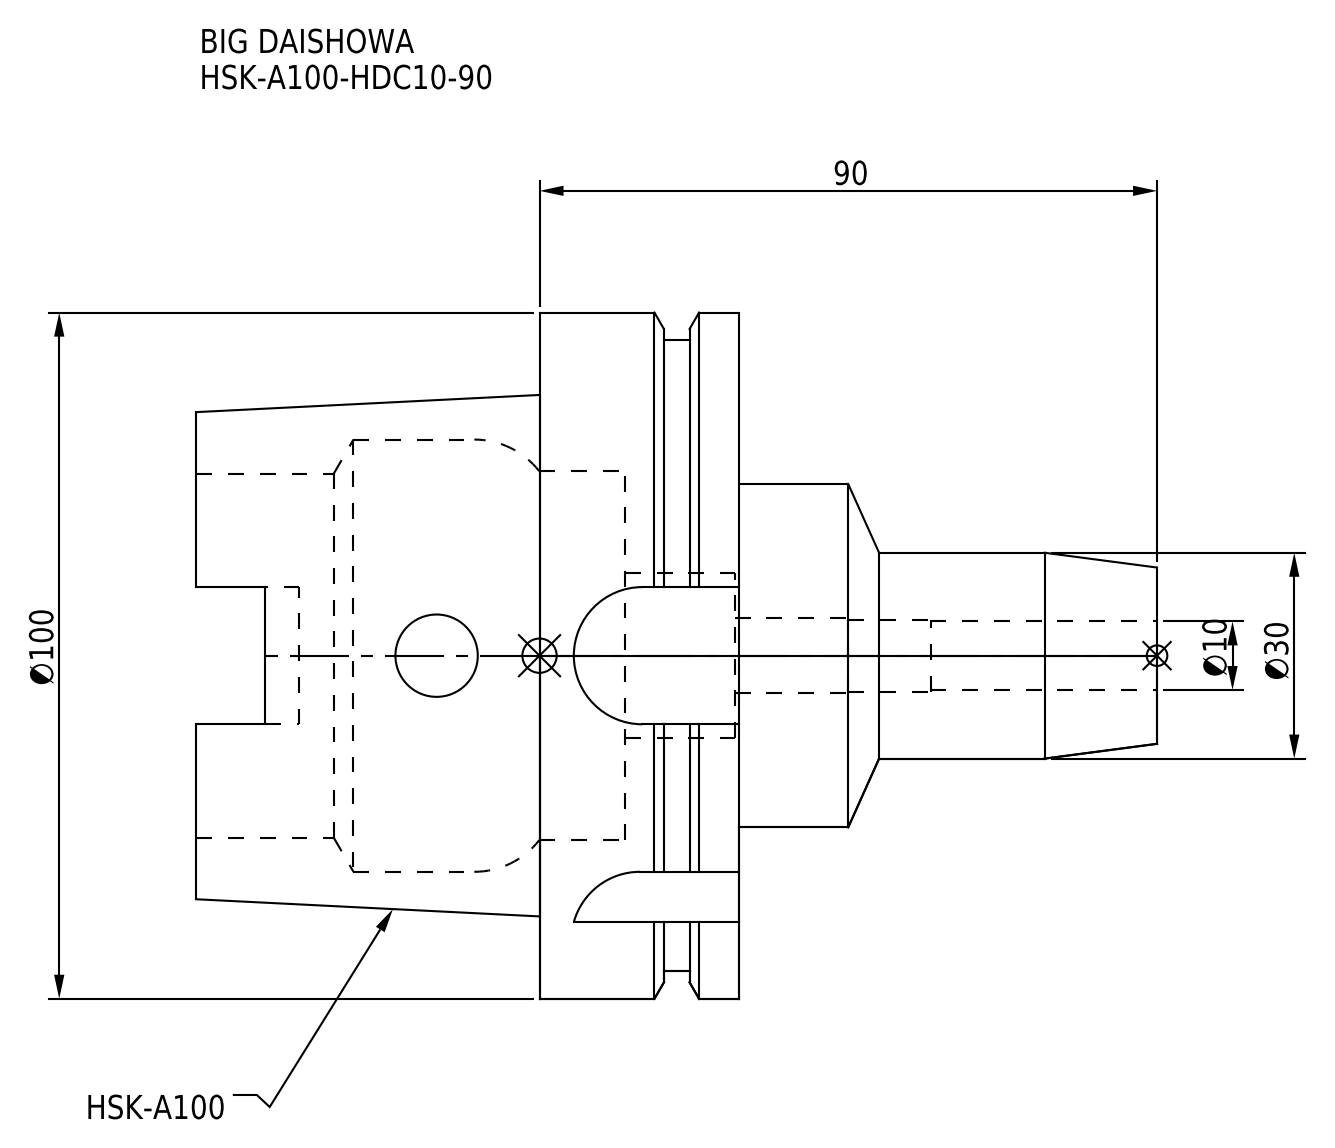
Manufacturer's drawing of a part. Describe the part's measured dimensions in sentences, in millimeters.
The part is named "HSK-A100-HDC10-90". Its 3-D file was written by "CREO PARAMETRIC BY PTC INC, 2016380 (AUTOMOTIVE_DESIGN)". It is 1 solid with 92 faces: 34 planar, 40 cylindrical and 18 other. Overall it measures 140 by 100 by 100 millimeters. Its volume is 312 518 cubic millimeters and its surface area 58 007 square millimeters. Round holes: 1 of diameter 10, 1 of diameter 10.5, 1 of diameter 11, 1 of diameter 12, 1 of diameter 24, 1 of diameter 53, 1 of diameter 53.8, 1 of diameter 63. Round bosses or shafts: 1 of diameter 100, 1 of diameter 92, 1 of diameter 50, 1 of diameter 30. Partial cylindrical surfaces (rounded edges, fillets, slot ends): 4 of radius 4.88, 4 of radius 10. The main face-to-face distances are 29, 16.55, 12.45, 79, 62.45, 50, 68.12, 71.88, 61, 77.55.
